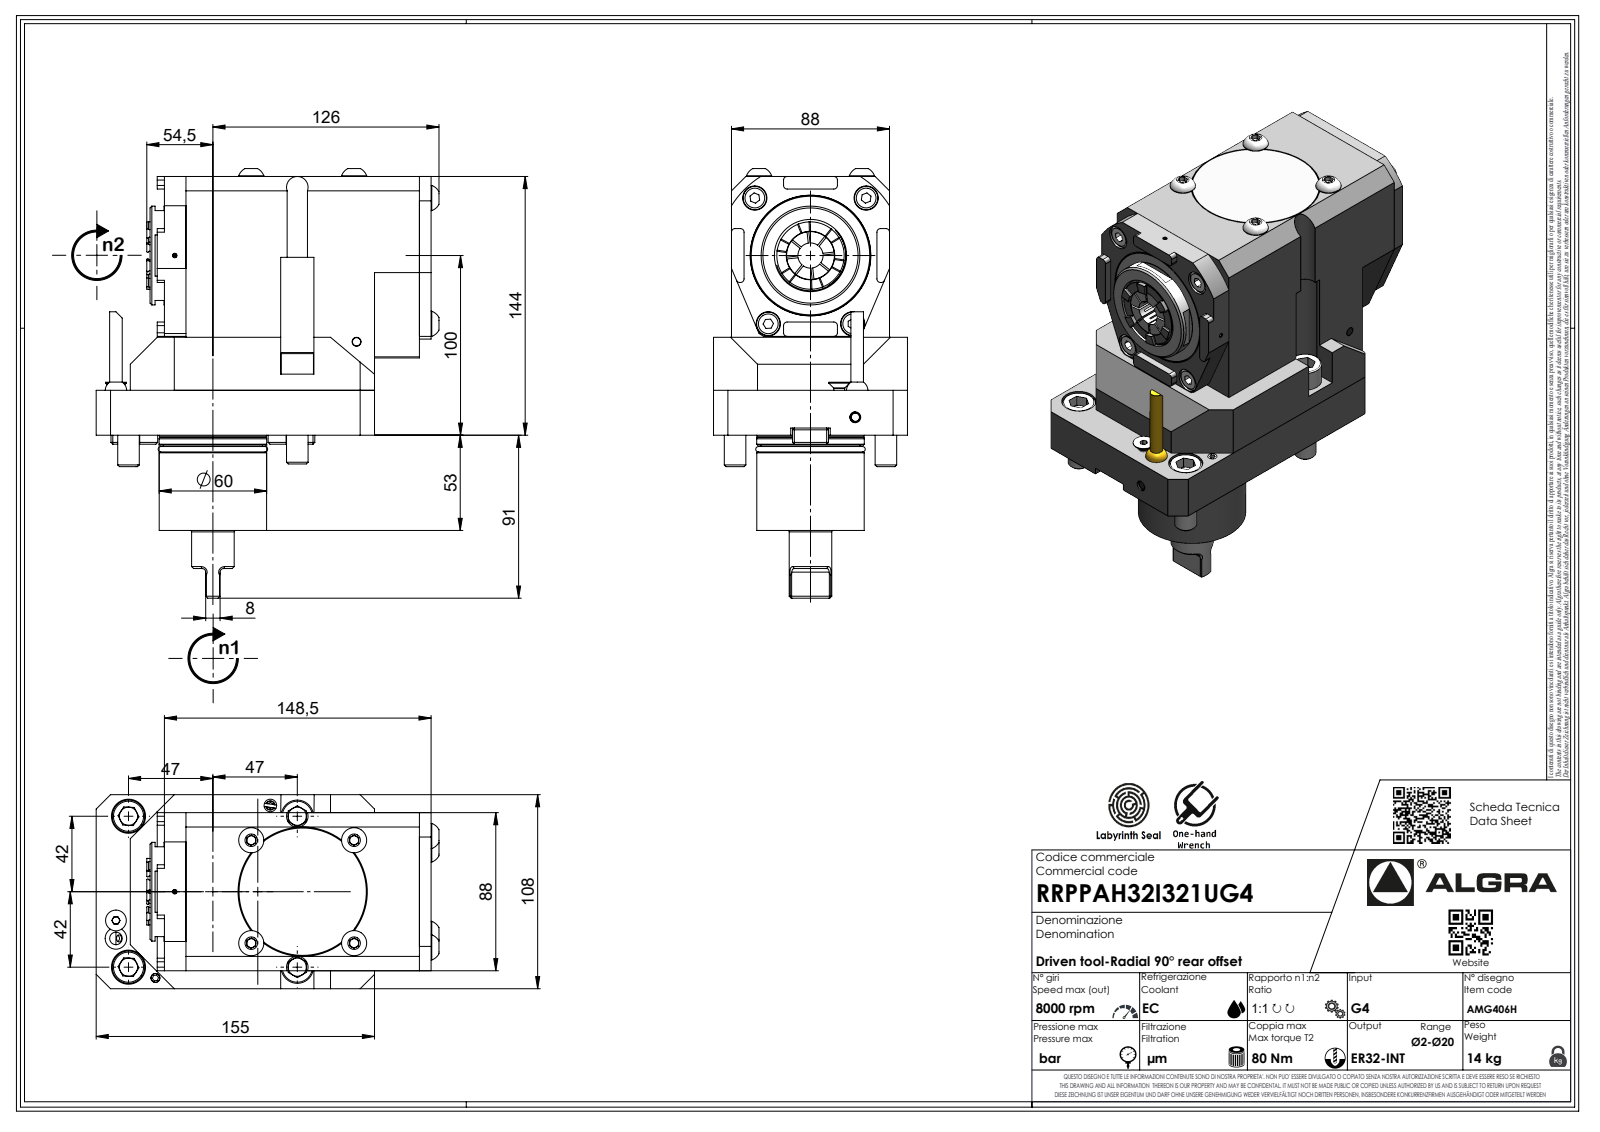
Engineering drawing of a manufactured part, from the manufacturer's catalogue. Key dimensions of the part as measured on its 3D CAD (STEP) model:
Part name (STEP PRODUCT): RRPPAH32I321UG4
STEP written by: SolidWorks 2023 (AUTOMOTIVE_DESIGN)
Units: millimetres
Bodies: 1 solid, 560 faces (352 planar, 85 cylindrical, 123 other)
Overall size (bounding box): 235 × 186.5 × 108
Volume: 2 136 000 mm³ · Surface area: 132 448 mm²
Round holes (diameter × count): ⌀12 ×2, ⌀2.1 ×1, ⌀4 ×1
Round bosses / shafts (diameter × count): ⌀18 ×2, ⌀12 ×2, ⌀59.9 ×1, ⌀59.8 ×1, ⌀59.5 ×1, ⌀55.2 ×1, ⌀55 ×1, ⌀23.7 ×1
Partial cylindrical surfaces — rounded edges, fillets, slot ends (radius × count): R2 ×19, R0.33 ×7, R0.52 ×7, R3.7 ×7, R1 ×2, R9.25 ×2, R0.21 ×1, R13.5 ×1
Main face-to-face distances: 98, 10, 144, 88, 108, 31.5, 148.5, 117, 30, 89.5
Hole centre spacings: 84
